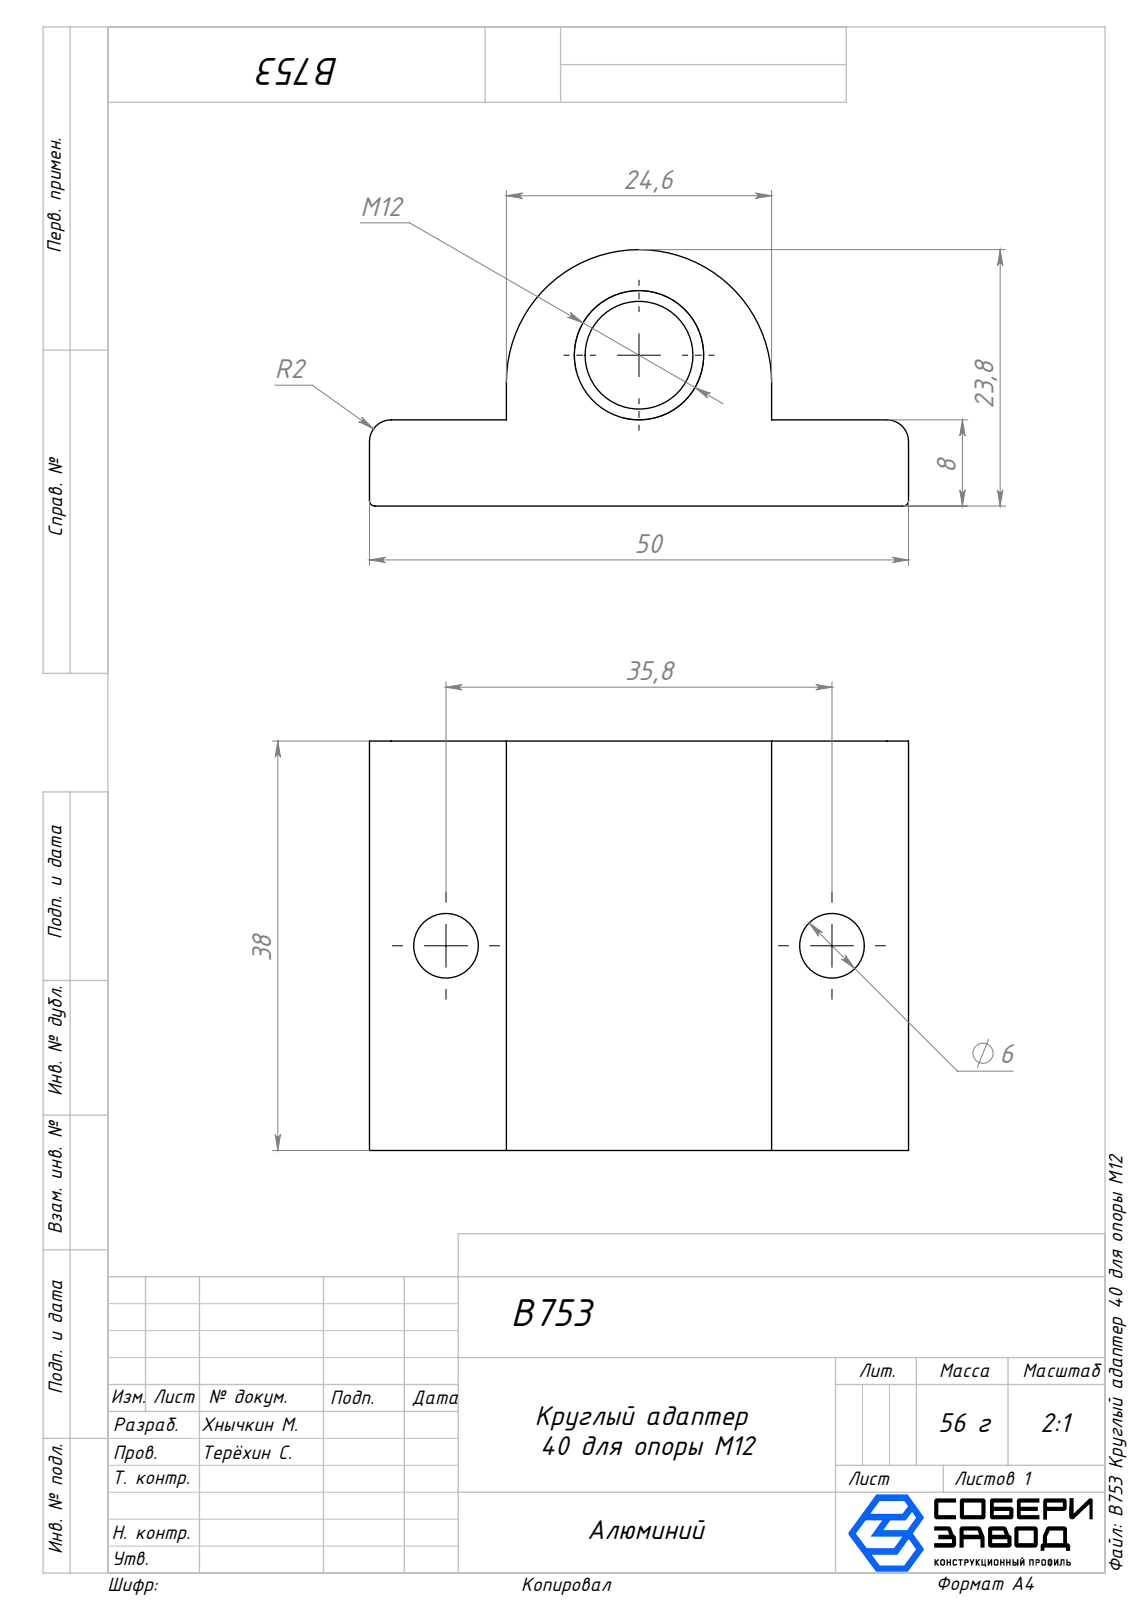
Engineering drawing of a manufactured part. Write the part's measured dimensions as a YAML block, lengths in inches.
part_name: "B753 Круглый адаптер 40 для опоры М12"
step_written_by: "SolidWorks 2025 (AUTOMOTIVE_DESIGN)"
units: inches
bodies: {solids: 1, faces: 24, planar: 9, cylindrical: 11, other: 4}
overall_size: [1.969, 1.496, 0.937]
volume: 1.462
surface_area: 12.03
round_holes:
  - {diameter: 0.236, count: 2}
  - {diameter: 0.394, count: 1}
partial_cylinders:
  - {radius: 0.02, count: 2}
  - {radius: 0.079, count: 2}
  - {radius: 0.484, count: 1}
face_to_face_distances: [0.315, 1.496, 0.5, 1.469, 1.969, 0.969]
hole_center_spacings: [1.409]
